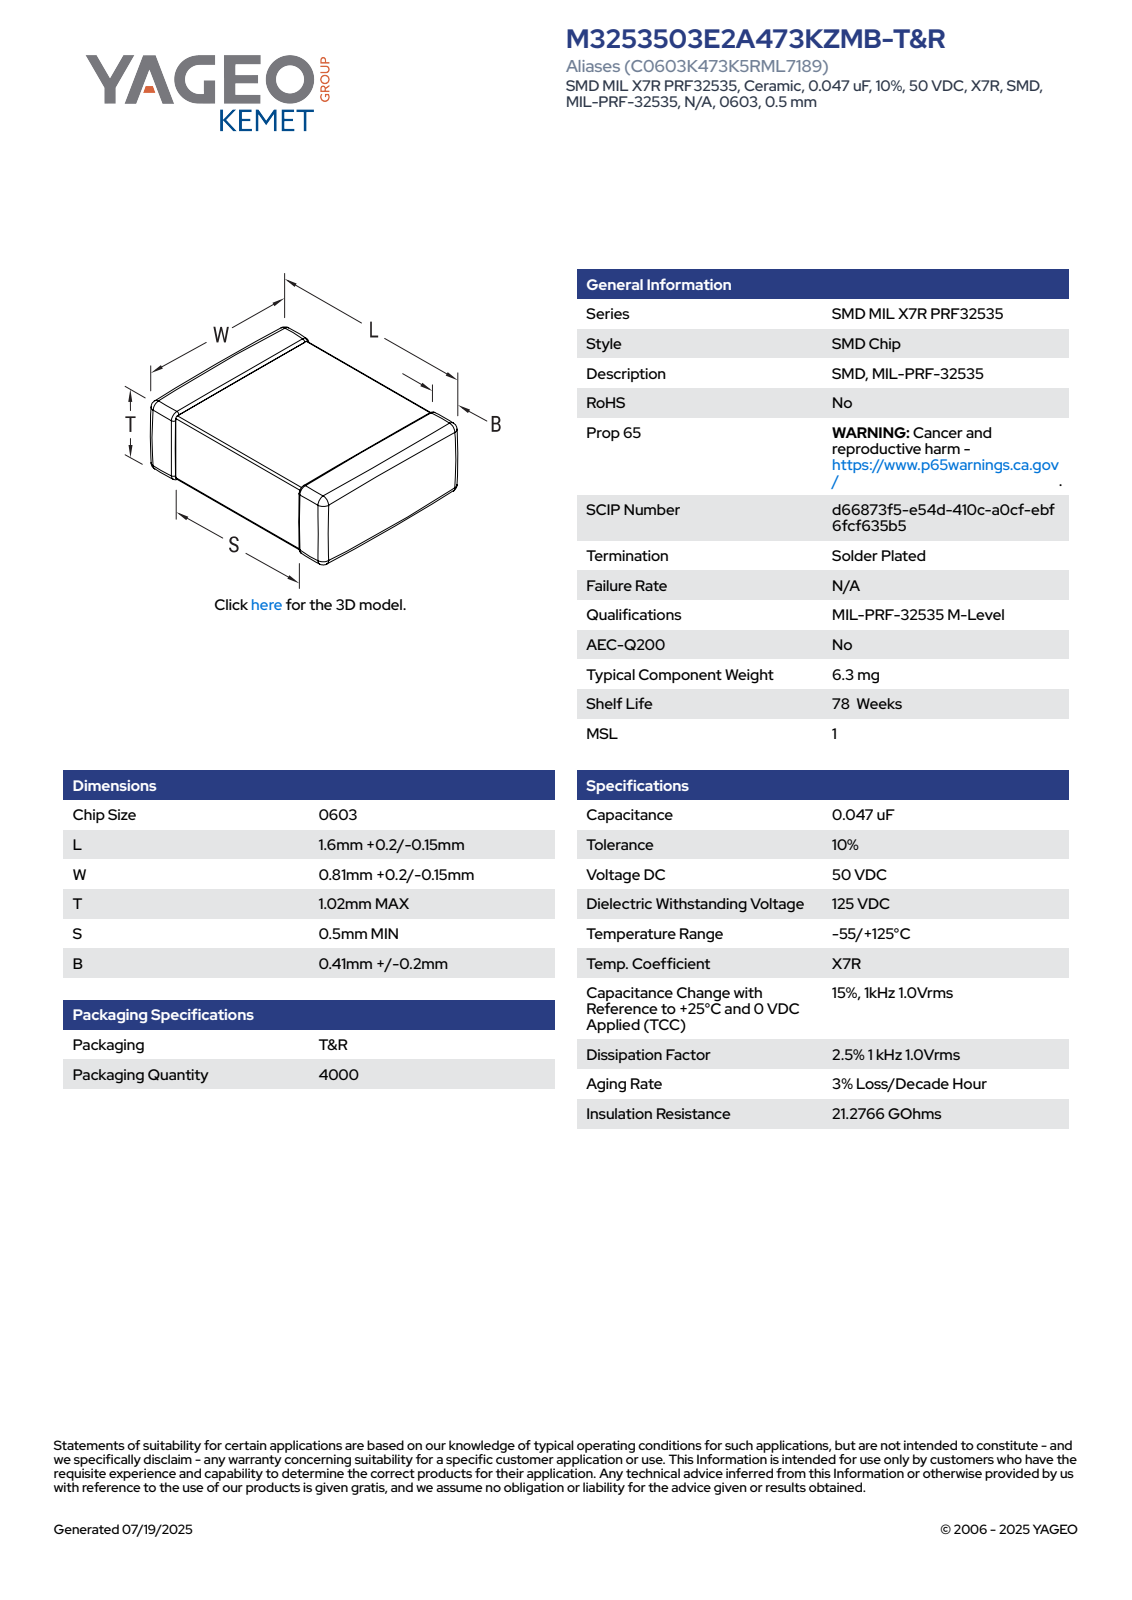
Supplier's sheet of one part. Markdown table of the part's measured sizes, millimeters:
| quantity | value |
| --- | --- |
| part name | CCSM_STD_0603_L0.2W0.2T1.02S1.02B0.61 |
| STEP written by | SolidWorks 2021 (AUTOMOTIVE_DESIGN) |
| units | millimeters |
| bodies | 4 solids, 125 faces (71 planar, 38 cylindrical, 16 other) |
| overall size | 1.8 × 1.02 × 1.01 |
| volume | 2 mm³ |
| surface area | 9 mm² |
| main face-to-face distances | 1, 1.01, 1.02, 0.99, 1.8, 0.97, 0.98, 0.82, 0.83, 0.4 |
